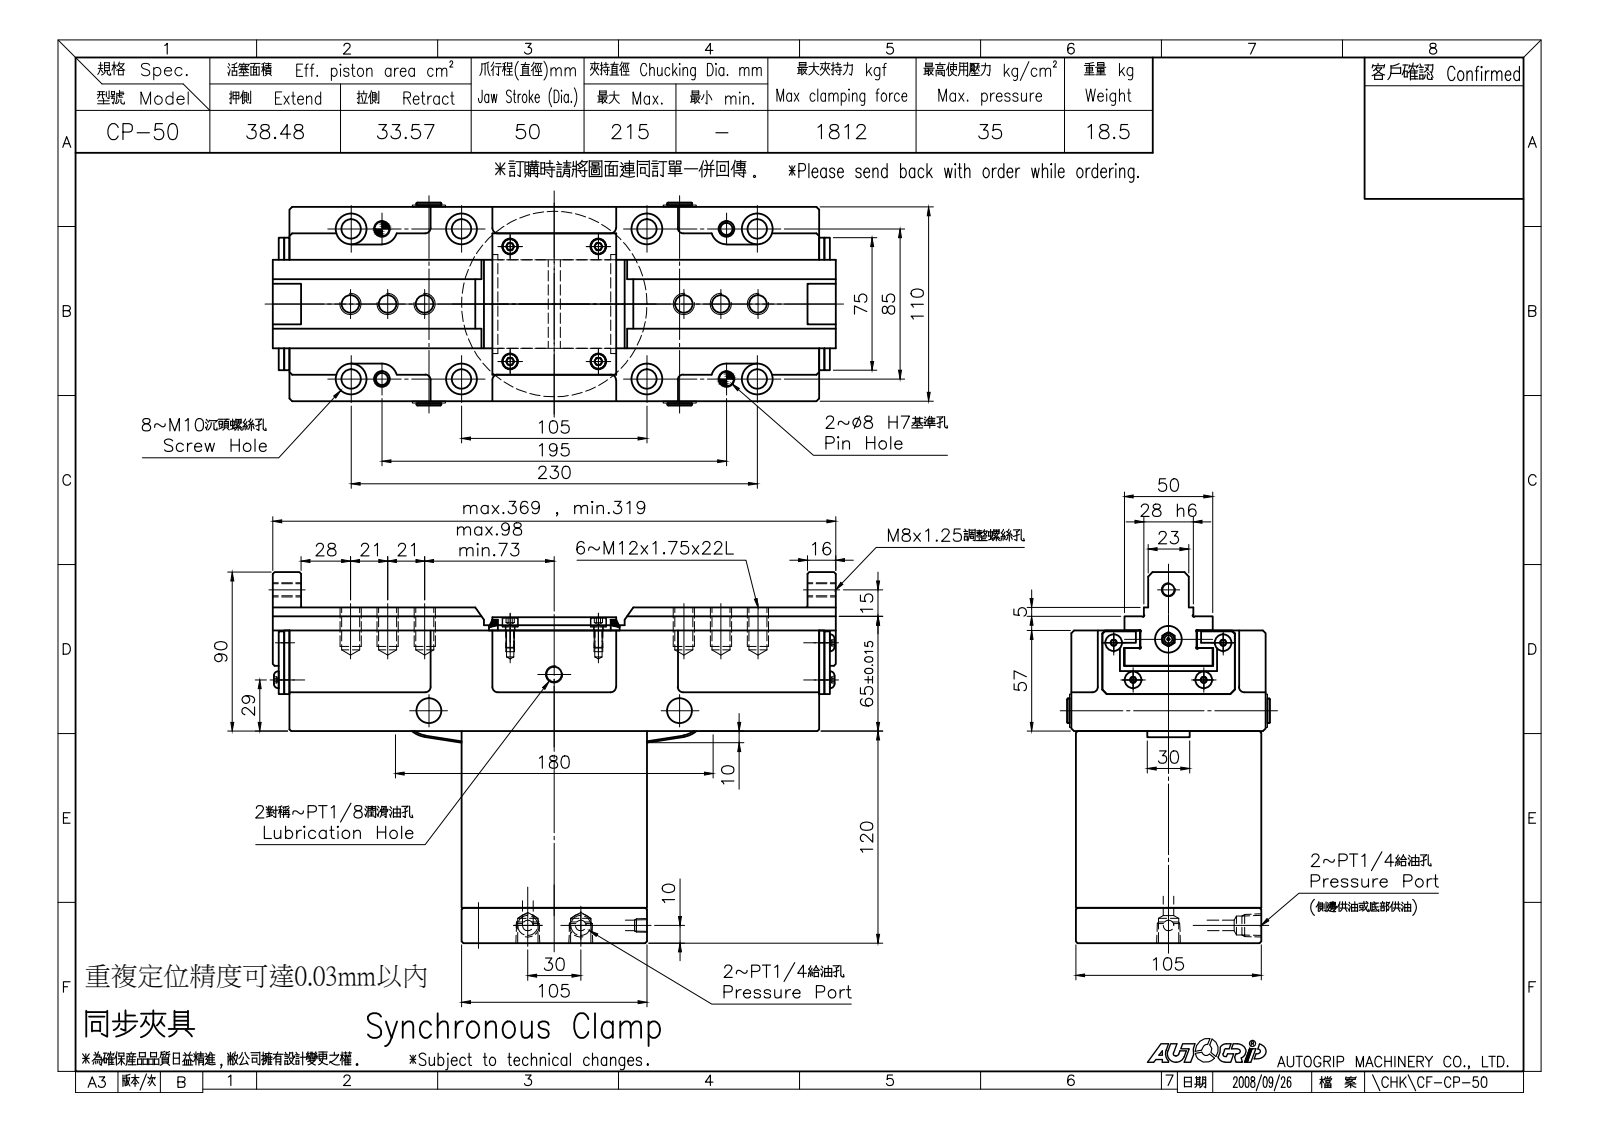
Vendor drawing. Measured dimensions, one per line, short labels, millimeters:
name: CF-CP-50-11000; CF-CP-50; CF-CP-50-10000; 圓頭內六角螺栓_M5x12 (+8 more)
written by: SolidWorks 2016 (CONFIG_CONTROL_DESIGN)
unit: mm
bodies: 26 solids, 1119 faces (546 planar, 381 cylindrical, 192 other)
size: 318.72 × 210 × 110
volume: 3 053 000 mm³; area: 410 926 mm²
holes: 12× ⌀9, 9× ⌀5, 8× ⌀4.2, 8× ⌀6, 8× ⌀11, 8× ⌀12, 8× ⌀17.5, 7× ⌀8, 7× ⌀10.2, 6× ⌀14, 4× ⌀5.5, 4× ⌀6.8
bosses: 4× ⌀17.5, 4× ⌀13, 4× ⌀10, 4× ⌀9.5, 4× ⌀8.5, 1× ⌀105, 1× ⌀69.81, 1× ⌀60
rounds: 15× R3, 4× R8.75, 2× R4, 2× R8, 2× R11.5, 1× R23
face distances: 15, 20, 157, 10, 37, 6, 80, 3, 57, 47
hole spacings: 85, 5.8, 17.5, 21, 25.18, 29.26, 32.91, 41
